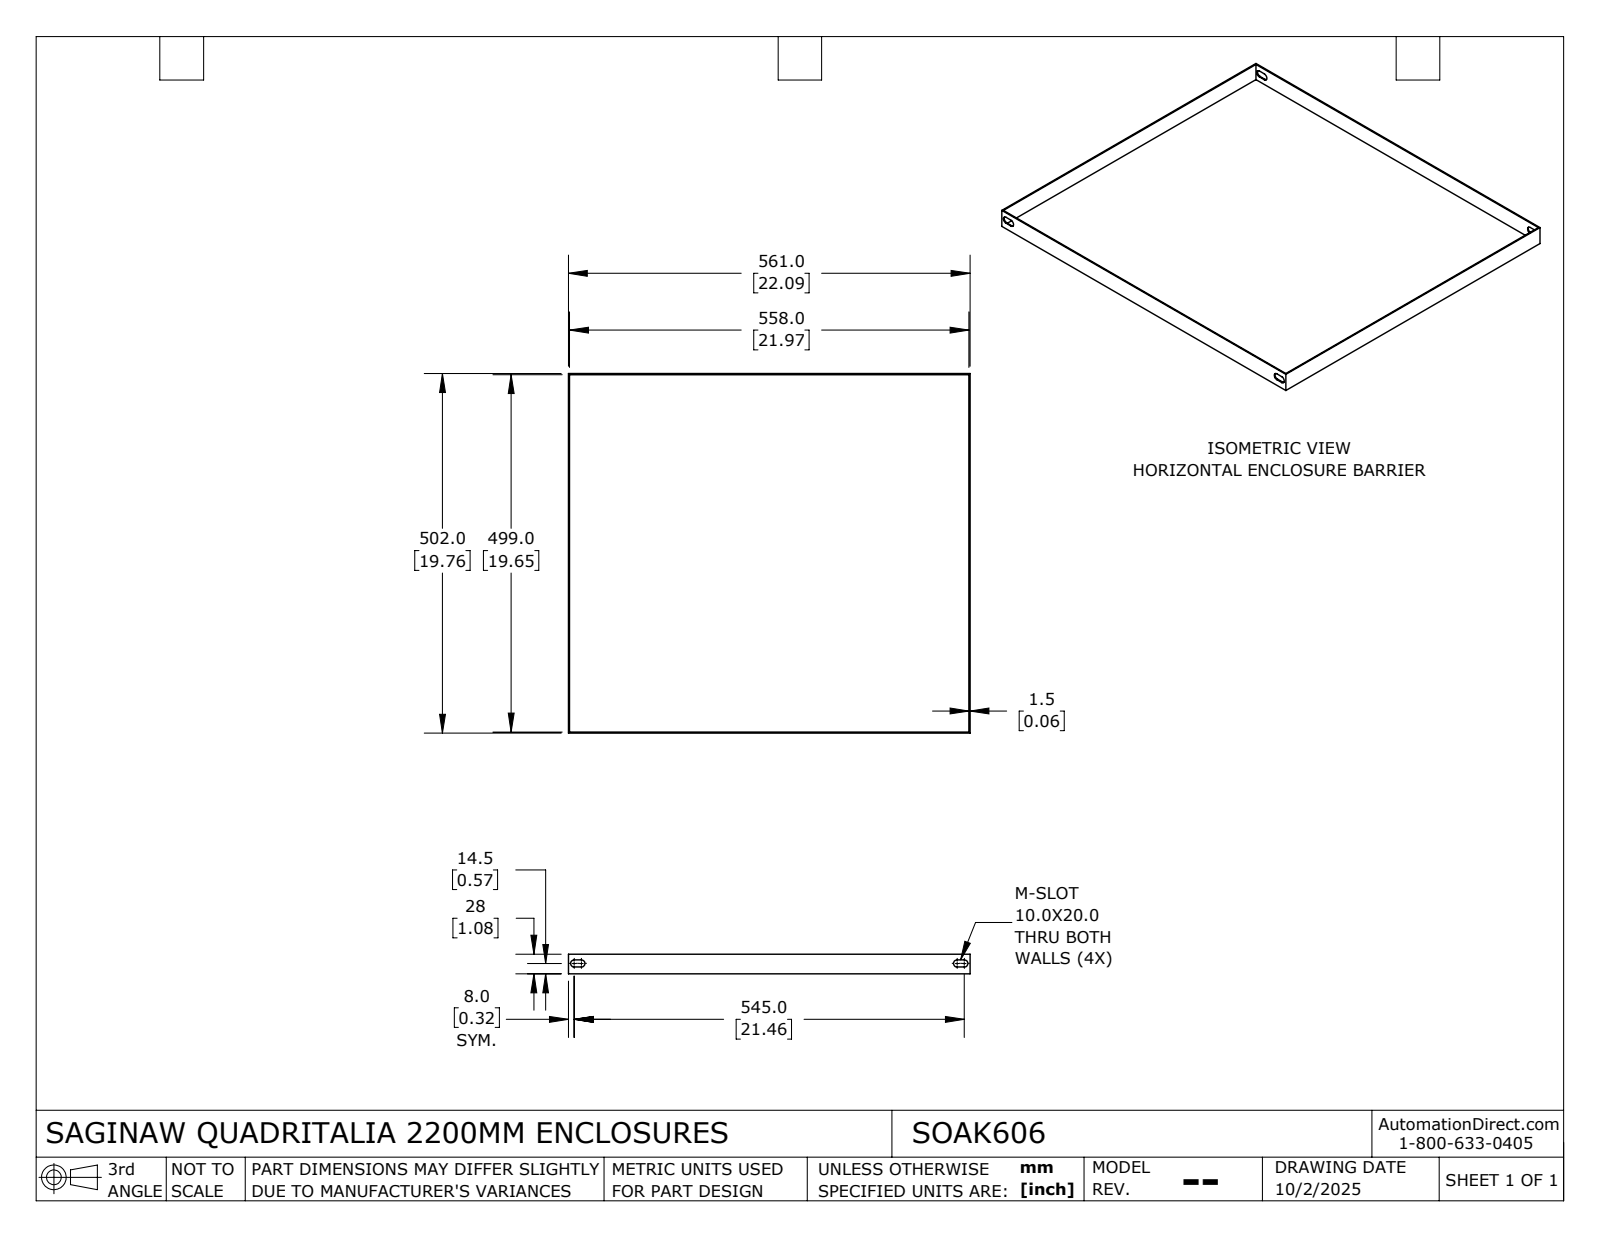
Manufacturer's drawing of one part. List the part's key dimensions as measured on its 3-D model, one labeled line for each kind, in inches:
Part name (STEP PRODUCT): SOAK606
STEP written by: SolidWorks 2024 (AUTOMOTIVE_DESIGN)
Units: inches
Bodies: 1 solid, 27 faces (19 planar, 8 cylindrical, 0 other)
Overall size (bounding box): 22.087 × 19.764 × 1.083
Volume: 30.76 in³ · Surface area: 1 047 in²
Partial cylindrical surfaces — rounded edges, fillets, slot ends (radius × count): R0.197 ×4
Main face-to-face distances: 0.059, 19.705, 22.028, 19.764, 19.646, 22.087, 21.969, 1.083, 1.024, 0.315
